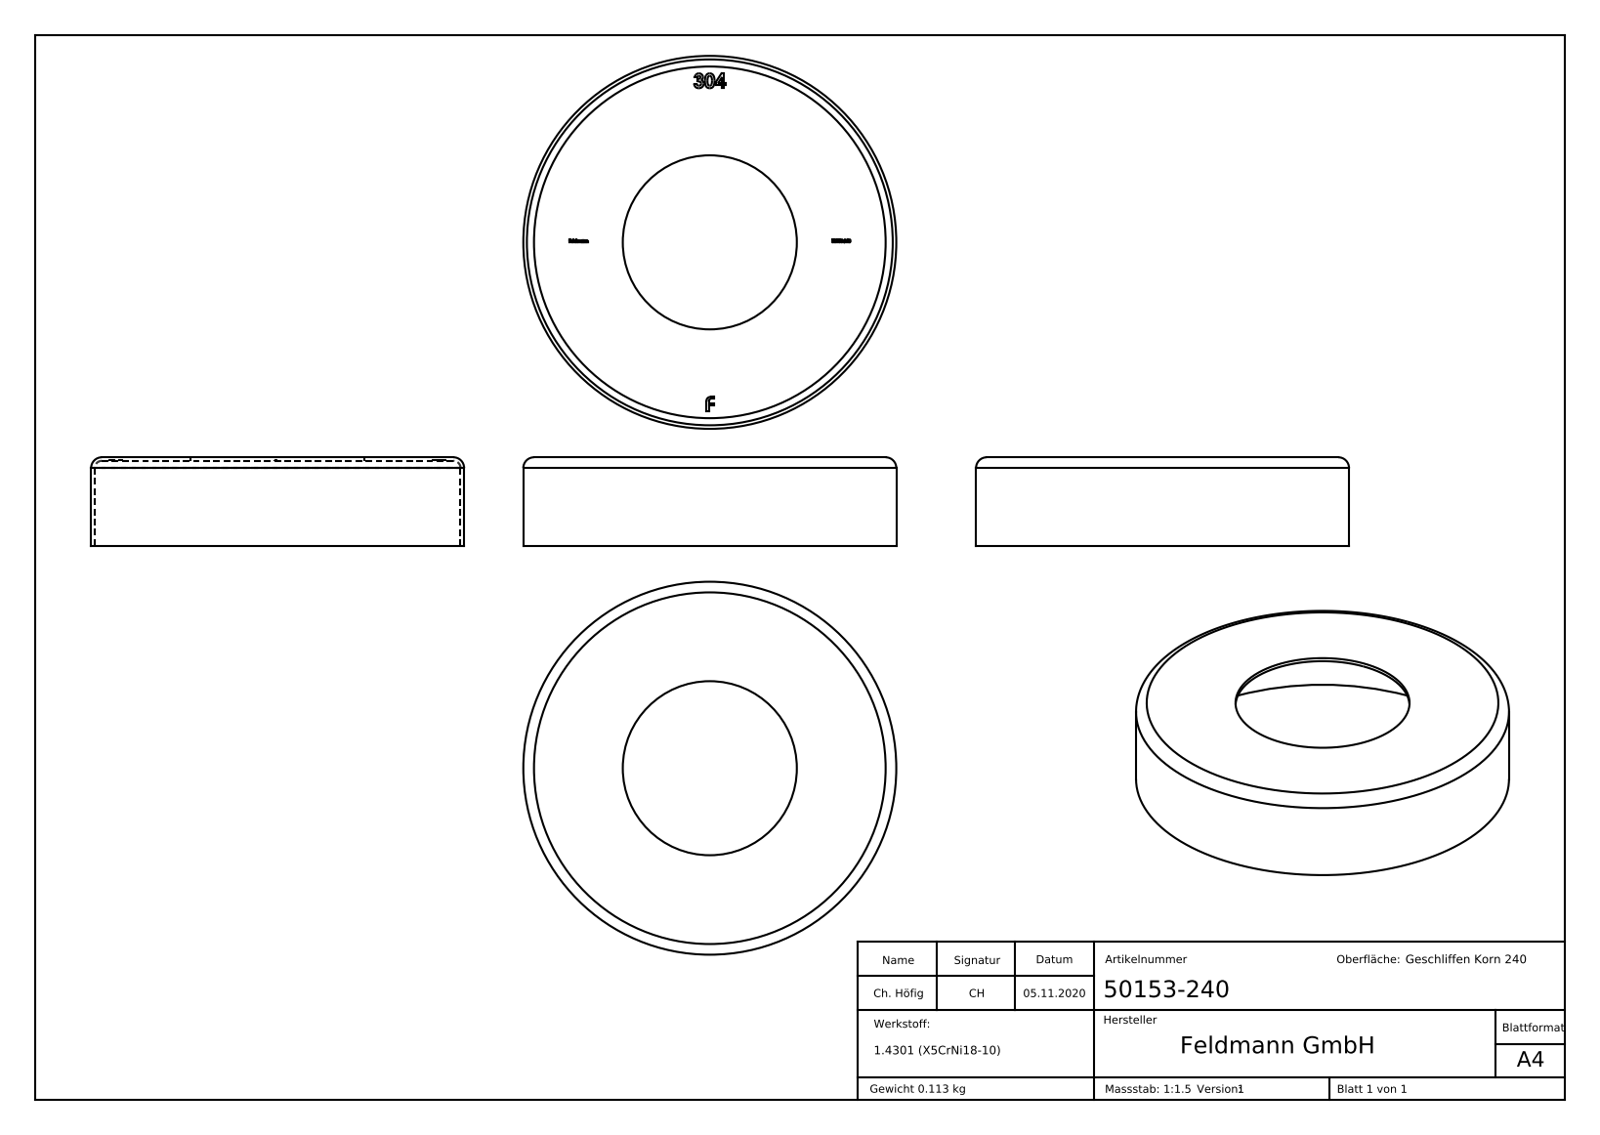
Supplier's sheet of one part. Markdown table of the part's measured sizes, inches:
| quantity | value |
| --- | --- |
| part name | 50153-240 |
| STEP written by | SolidWorks 2018 (CONFIG_CONTROL_DESIGN) |
| units | inches |
| bodies | 1 solid, 294 faces (157 planar, 6 cylindrical, 131 other) |
| overall size | 4.134 × 4.134 × 0.984 |
| volume | 0.87 in³ |
| surface area | 44.98 in² |
| round holes (diameter × count) | 1.929 × 1, 4.055 × 1 |
| round bosses / shafts (diameter × count) | 4.134 × 1 |
| main face-to-face distances | 0.039, 0.945, 0.984, 0.949, 0.035, 0.028, 0.197, 0.169, 0.023, 0.027 |
